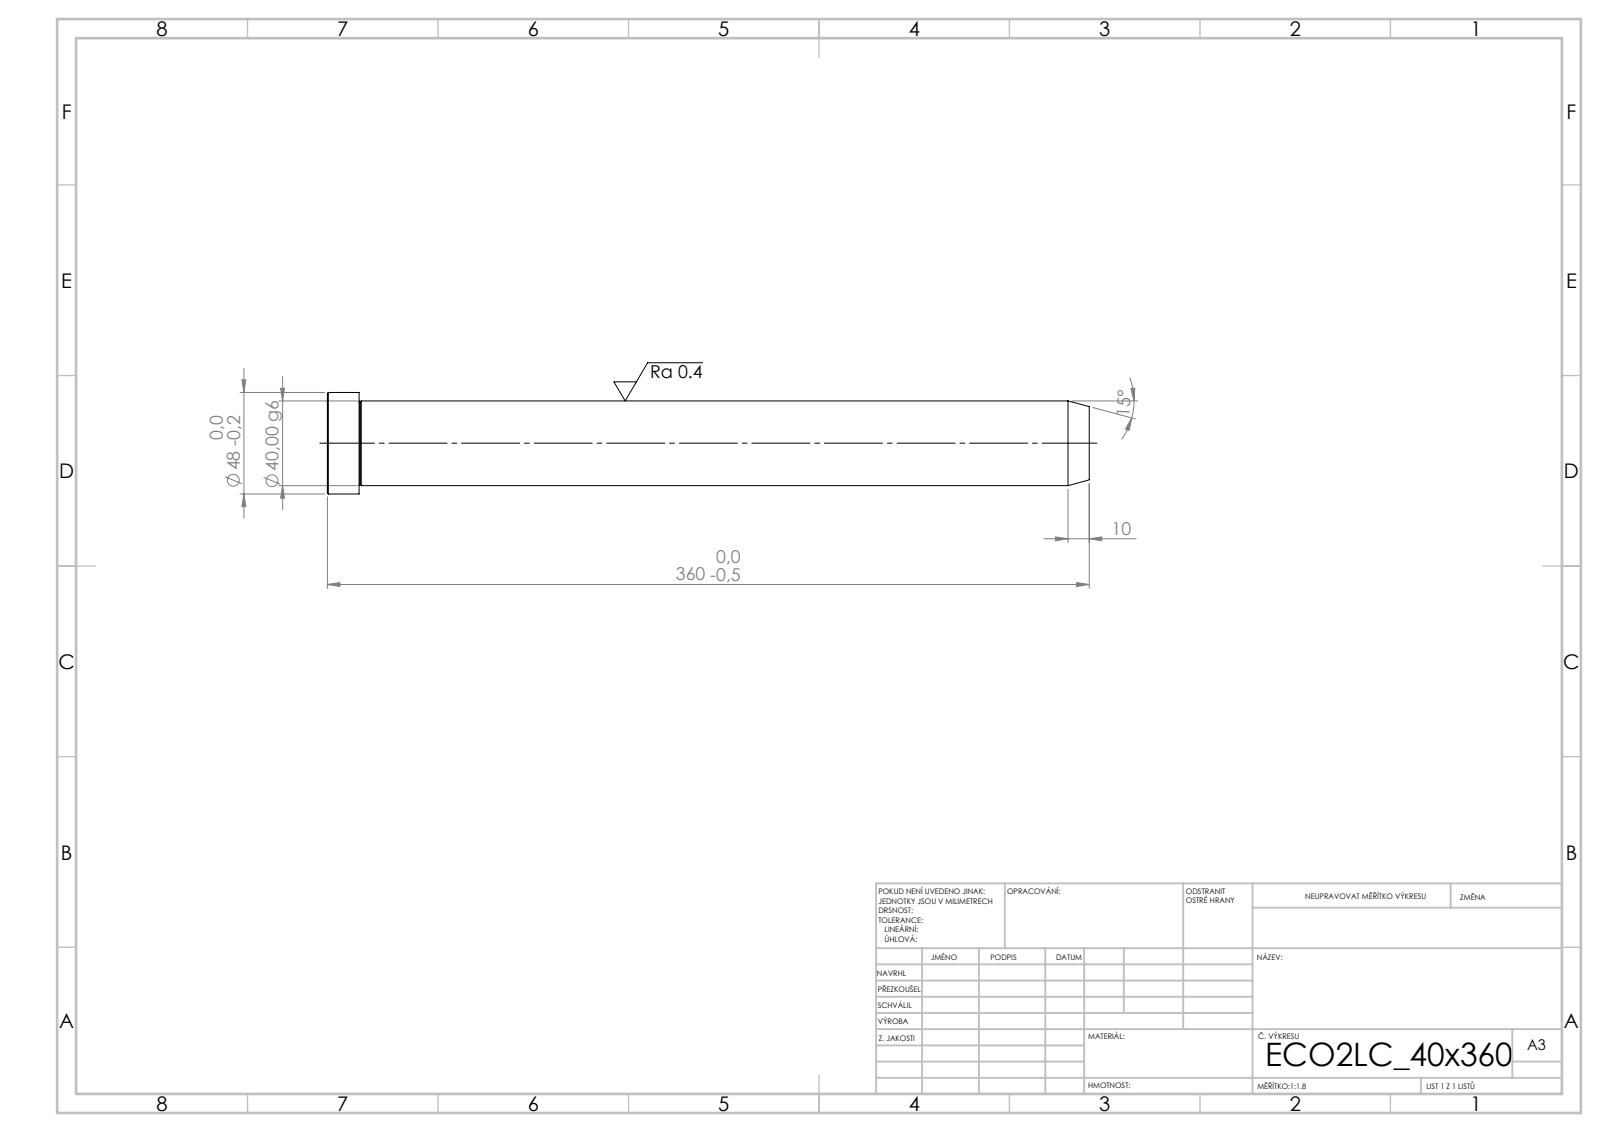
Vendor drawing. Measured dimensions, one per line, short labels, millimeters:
written by: SolidWorks 2019 (CONFIG_CONTROL_DESIGN)
unit: mm
bodies: 1 solid, 15 faces (3 planar, 4 cylindrical, 8 other)
size: 360 × 48 × 48
volume: 459 007 mm³; area: 48 902 mm²
bosses: 1× ⌀48, 1× ⌀40
face distances: 360, 345, 15
